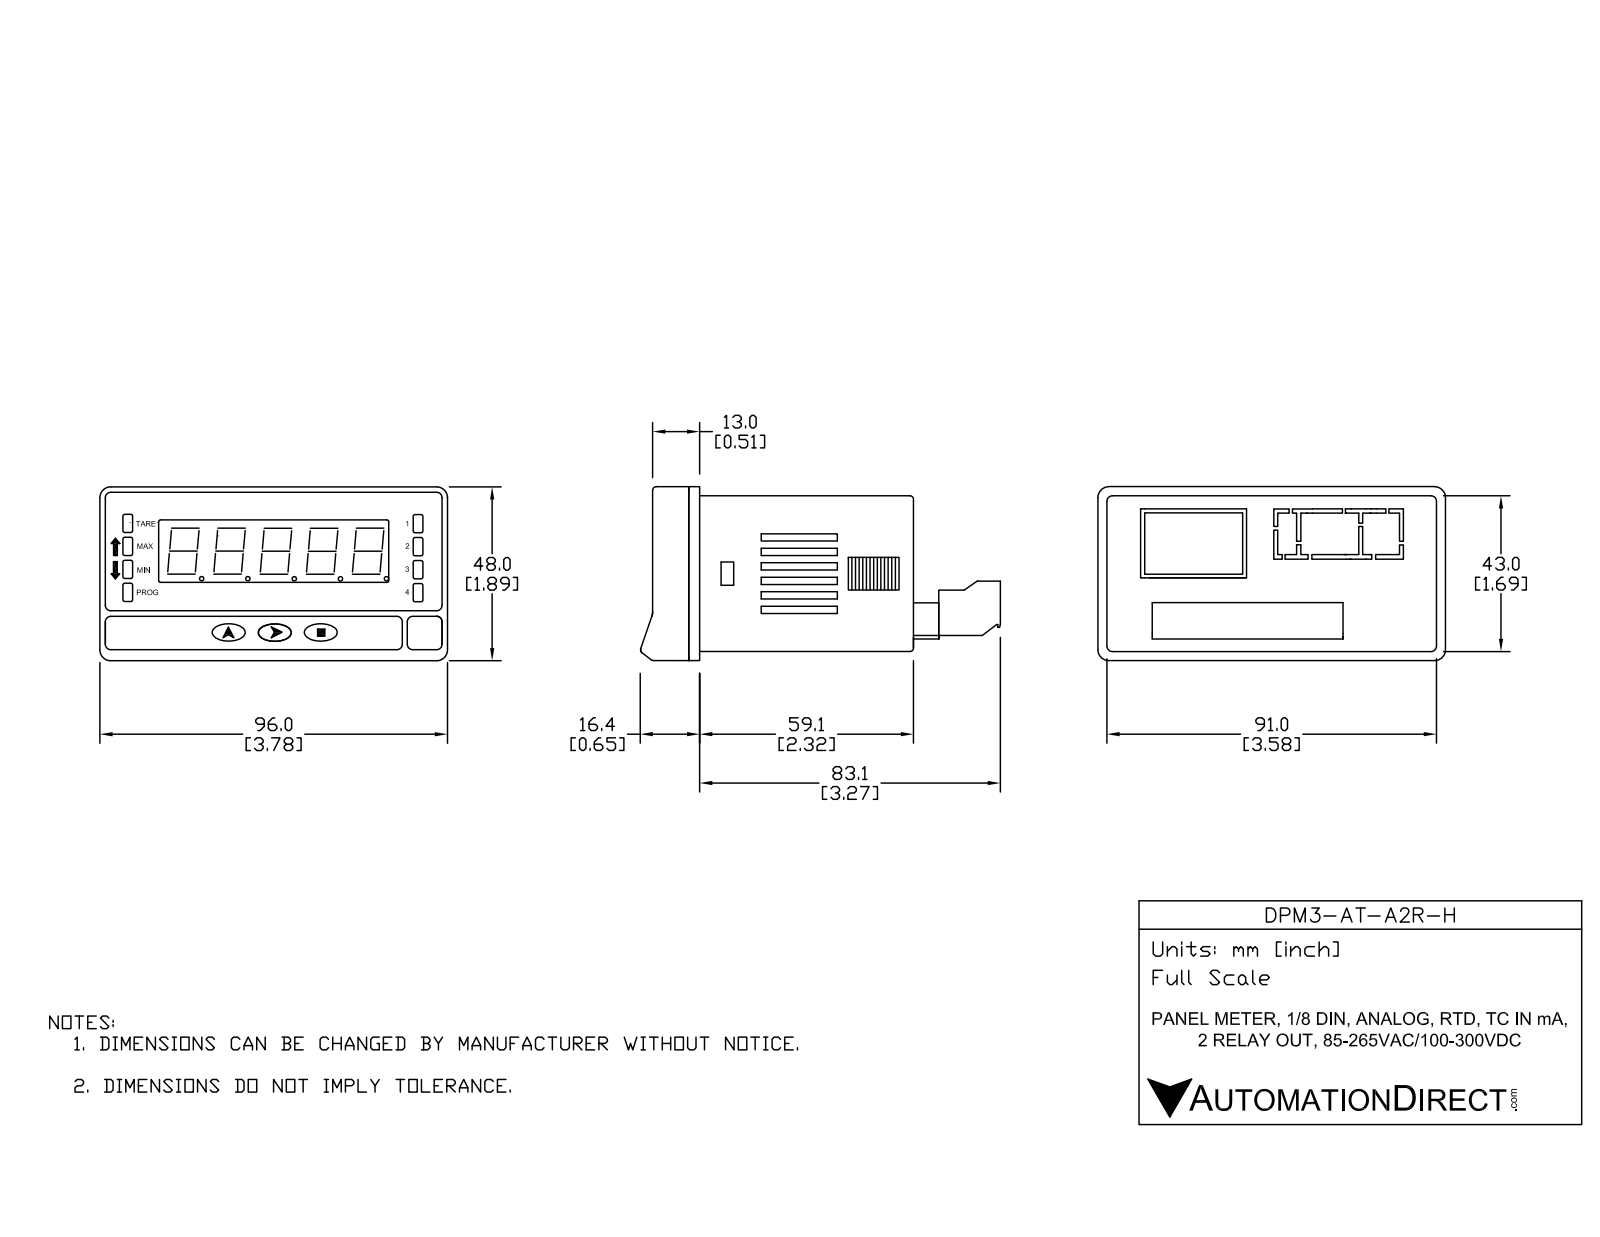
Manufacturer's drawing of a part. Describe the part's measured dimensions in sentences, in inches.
The part is named "DPM3-AT-A2R-H". Its 3-D file was written by "SolidWorks 2017 (AUTOMOTIVE_DESIGN)". It is 10 solids with 2622 faces: 2041 planar, 368 cylindrical and 213 other. Overall it measures 3.916 by 3.78 by 1.89 inches. Its volume is 5.643 cubic inches and its surface area 104.7 square inches. Round holes: 12 of diameter 0.039, 12 of diameter 0.079, 10 of diameter 0.078, 10 of diameter 0.118, 10 of diameter 0.152. Round bosses or shafts: 5 of diameter 0.047. Partial cylindrical surfaces (rounded edges, fillets, slot ends): 53 of radius 0.004, 42 of radius 0.02, 24 of radius 0.012, 24 of radius 0.014, 12 of radius 0.07, 12 of radius 0.072, 10 of radius 0.118, 10 of radius 0.121. The main face-to-face distances are 0.059, 1.634, 0.098, 1.693, 1.575, 1.732, 3.524, 0.433, 0.157, 2.78. The hole center spacings are 0.138, 0.276, 0.201, 0.413, 0.748, 0.197, 0.197, 0.201.
